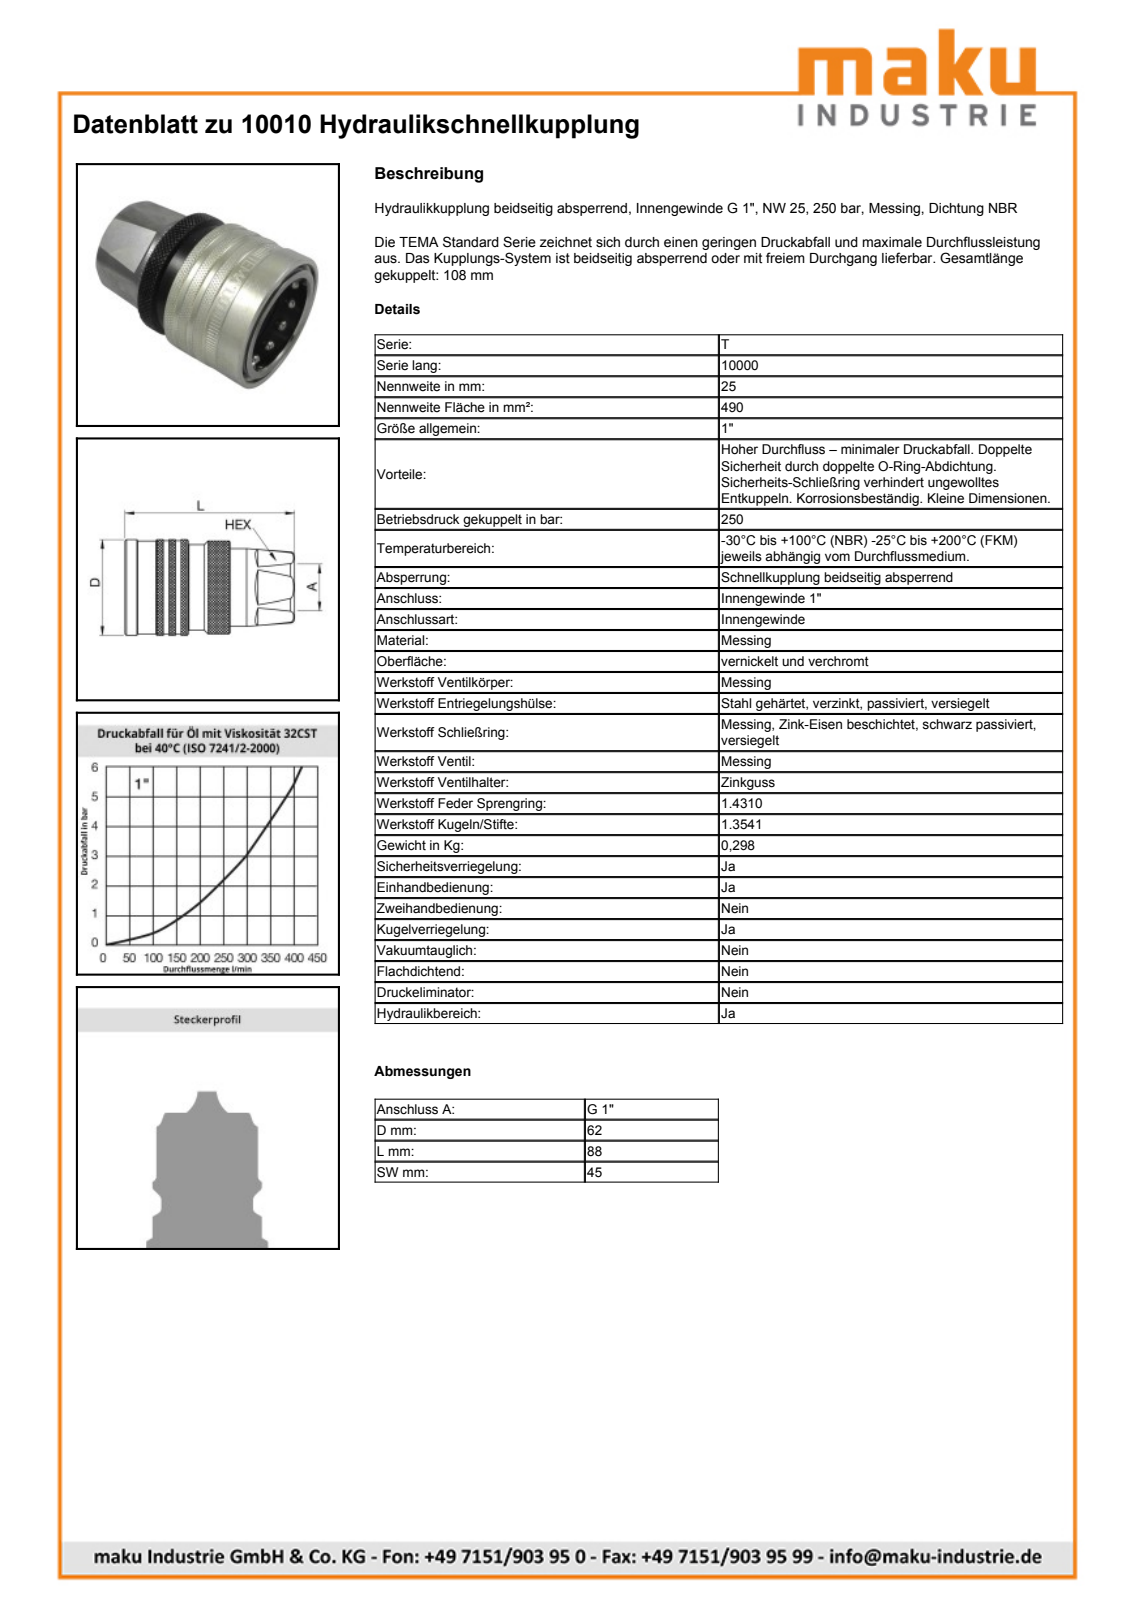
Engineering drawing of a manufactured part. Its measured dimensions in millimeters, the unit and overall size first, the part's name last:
Units: millimetres
Overall size (bounding box): 88.3 × 62 × 62
Round holes (diameter × count): ⌀24.4 ×1, ⌀30.6 ×1, ⌀41 ×1, ⌀41 ×1, ⌀43.4 ×1, ⌀44.1 ×1, ⌀47.3 ×1, ⌀53 ×1, ⌀55.2 ×1, ⌀56.4 ×1
Round bosses / shafts (diameter × count): ⌀62 ×1, ⌀61 ×1, ⌀60.7 ×1, ⌀59 ×1, ⌀54.5 ×1, ⌀51.6 ×1, ⌀49.6 ×1
Main face-to-face distances: 45, 35.6, 31.2, 66.8, 21.5, 52.7, 88.3, 3.9, 48.8, 27.3
Volume: 149 826 mm³ · Surface area: 32 605 mm²
Bodies: 1 solid, 137 faces (33 planar, 42 cylindrical, 62 other)
Part name (STEP PRODUCT): 10010
STEP written by: SolidWorks 2009 (AUTOMOTIVE_DESIGN)
